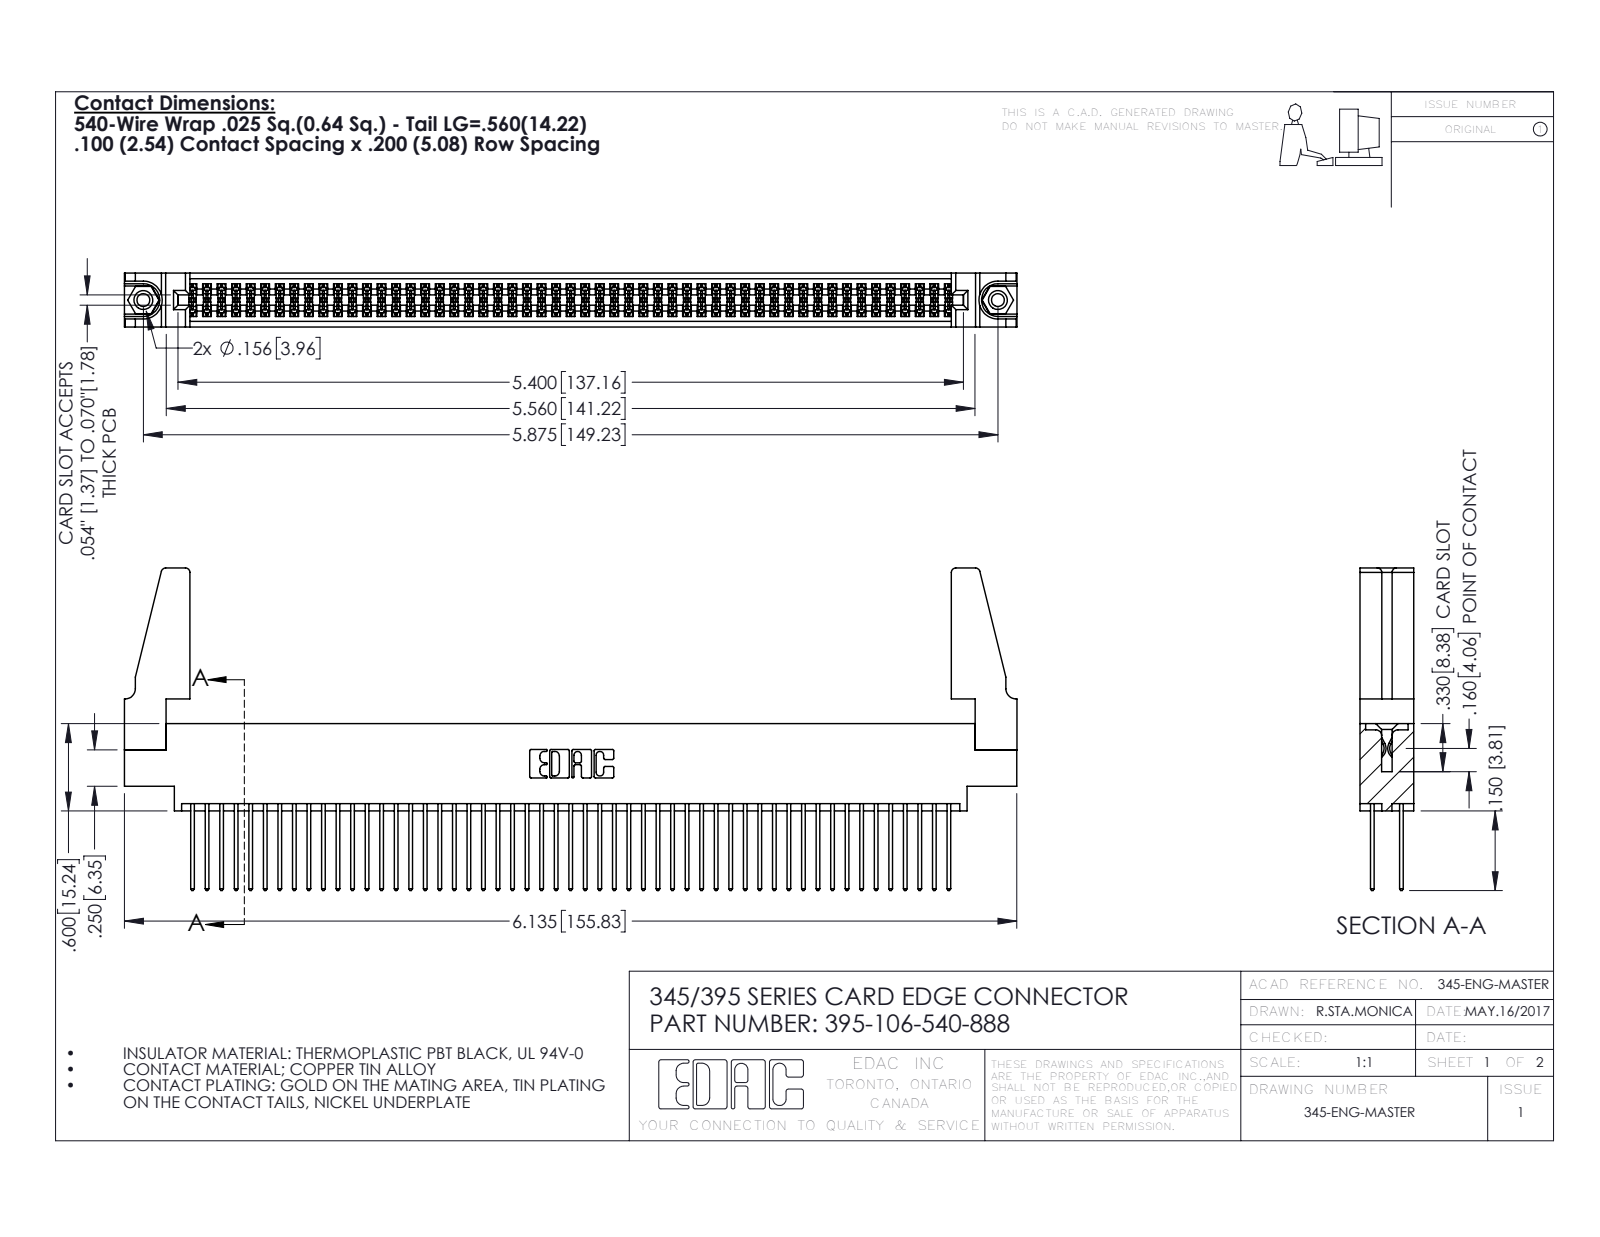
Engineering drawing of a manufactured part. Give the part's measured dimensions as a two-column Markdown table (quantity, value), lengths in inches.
| quantity | value |
| --- | --- |
| part name | 345 Part_0.170 Offset - 0.156 Dia-TH; 395-106-540-888; 345-292-001_345-293-140; 345-220-078_345-220-088 (+1 more) |
| STEP written by | SolidWorks 2016 (CONFIG_CONTROL_DESIGN) |
| units | inches |
| bodies | 111 solids, 5554 faces (3654 planar, 1884 cylindrical, 16 other) |
| overall size | 6.136 × 2.217 × 0.37 |
| volume | 1.146 in³ |
| surface area | 43.86 in² |
| round holes (diameter × count) | 0.089 × 2, 0.125 × 2, 0.156 × 2, 0.064 × 1 |
| round bosses / shafts (diameter × count) | 0.155 × 2 |
| partial cylindrical surfaces (radius × count) | 0.006 × 159, 0.01 × 106, 0.01 × 22, 0.03 × 8, 0.007 × 6, 0.031 × 6, 0.026 × 3, 0.014 × 2 |
| main face-to-face distances | 0.072, 0.298, 0.2, 0.098, 0.272, 0.025, 0.37, 0.225, 0.175, 0.149 |
| hole center spacings | 0.27, 5.639, 5.875 |
